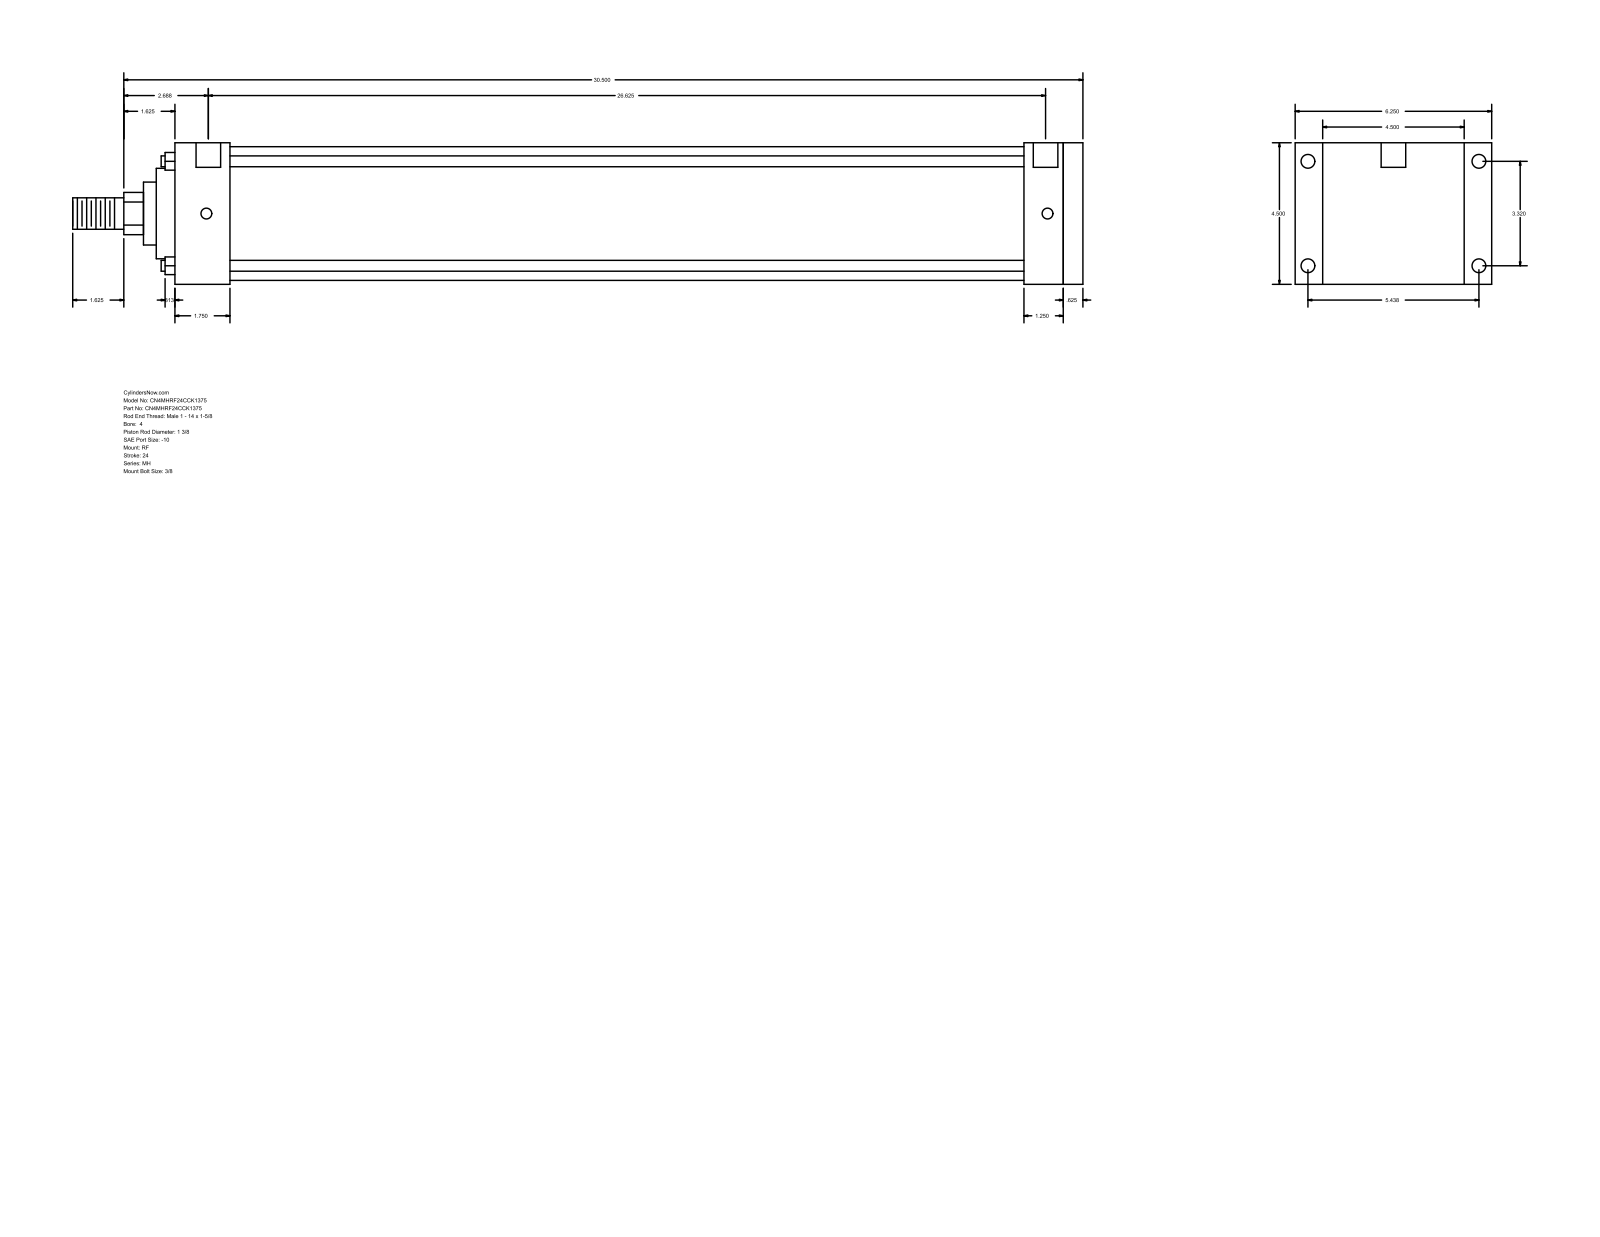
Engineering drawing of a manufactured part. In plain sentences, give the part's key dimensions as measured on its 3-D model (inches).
The part is named "MH_RF__0400_1.375". Its 3-D file was written by "GSSL Pune (CONFIG_CONTROL_DESIGN)". It is 0 solids with 94 faces: 65 planar, 29 cylindrical and 0 other. Overall it measures 32.125 by 6.25 by 4.5 inches. Round holes: 4 of diameter 0.344, 4 of diameter 0.438, 2 of diameter 0.781. Round bosses or shafts: 4 of diameter 0.345, 1 of diameter 4.25, 1 of diameter 2.875, 1 of diameter 2, 1 of diameter 1.375, 1 of diameter 1. Partial cylindrical surfaces (rounded edges, fillets, slot ends): 1 of radius 0.672. The main face-to-face distances are 4.5, 28.875, 28.25, 0.625, 1.75, 26.5, 27.125, 27, 25.25, 1.25. The hole center spacings are 3.32, 5.438, 6.371, 26.75, 0.062, 0.063, 26.625, 26.687.
